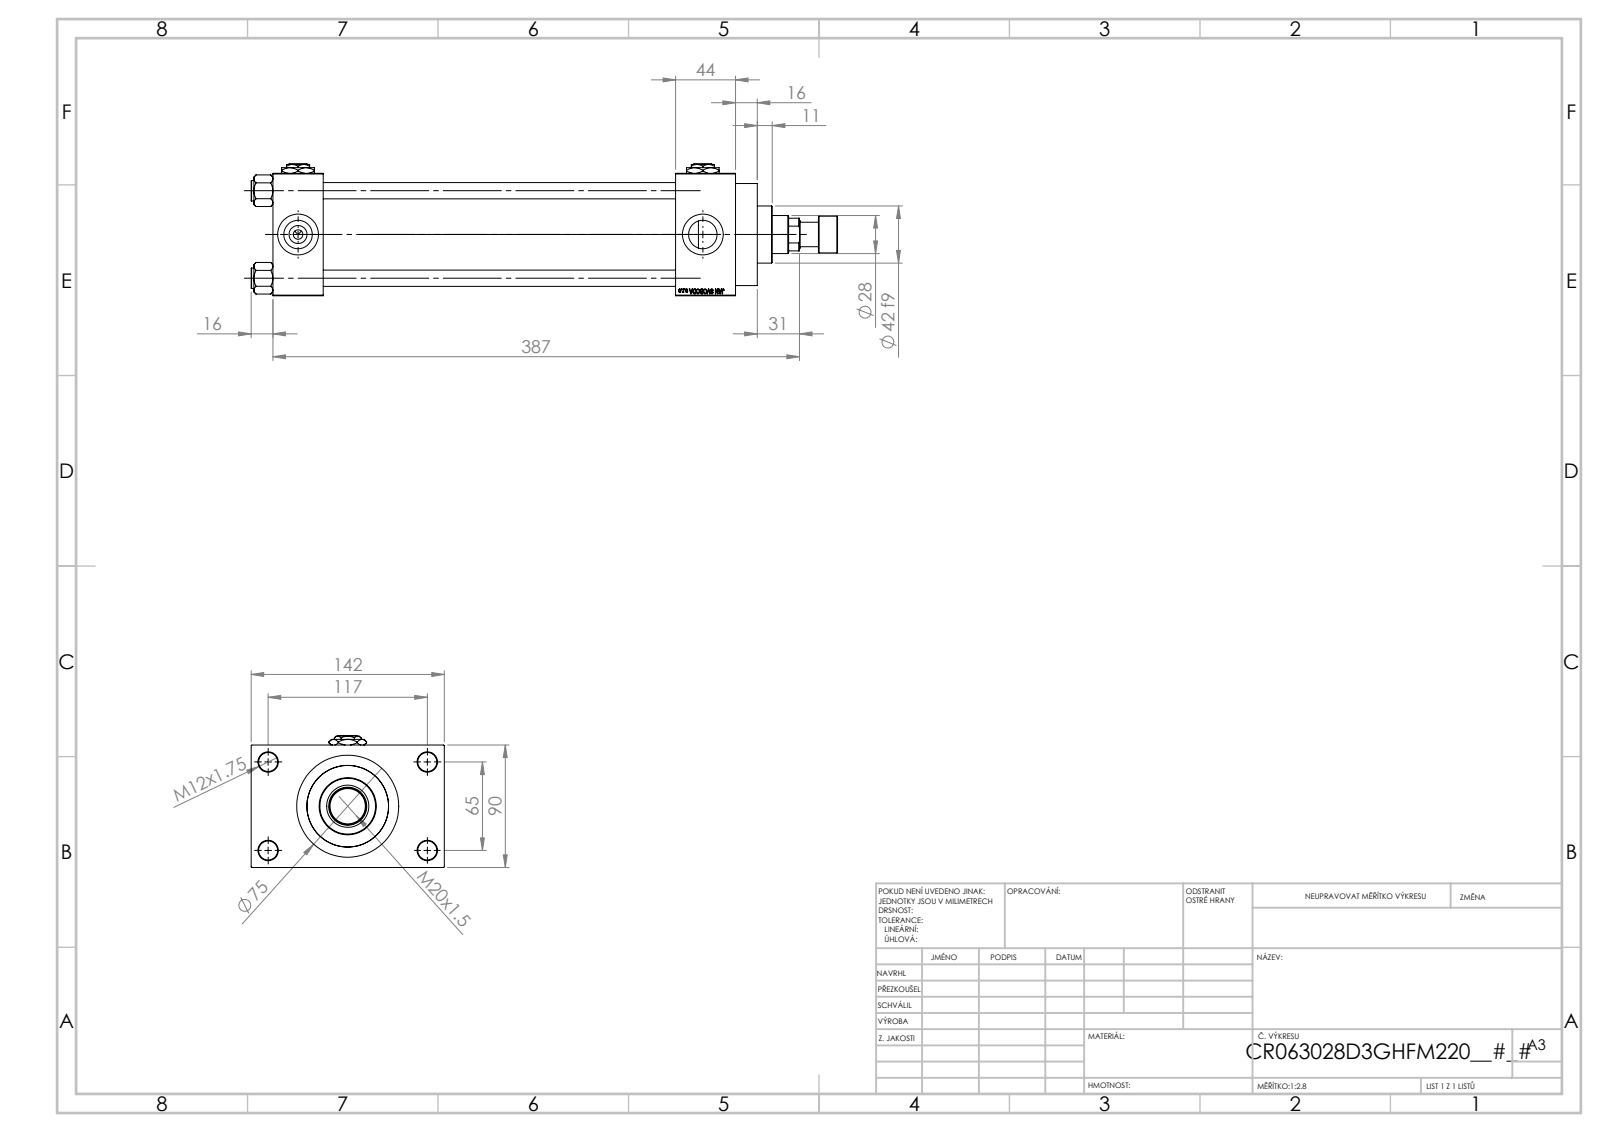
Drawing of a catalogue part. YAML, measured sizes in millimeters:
part_name: "V215CR_ROD_END_F; V215CR_D_Body; V215_VC_A; V215CR_D_TYCINKA (+3 more)"
step_written_by: "SolidWorks 2019 (CONFIG_CONTROL_DESIGN)"
units: millimeters
bodies: {solids: 14, faces: 1218, planar: 549, cylindrical: 103, other: 566}
overall_size: [431, 142, 97]
volume: 1440000
surface_area: 338888
round_holes:
  - {diameter: 12, count: 4}
  - {diameter: 14, count: 4}
  - {diameter: 20.96, count: 4}
  - {diameter: 30, count: 4}
  - {diameter: 7, count: 3}
  - {diameter: 18.5, count: 1}
  - {diameter: 28, count: 1}
  - {diameter: 31, count: 1}
  - {diameter: 50, count: 1}
  - {diameter: 60, count: 1}
  - {diameter: 63, count: 1}
round_bosses_or_shafts:
  - {diameter: 15, count: 4}
  - {diameter: 75, count: 1}
  - {diameter: 69, count: 1}
  - {diameter: 42, count: 1}
  - {diameter: 27, count: 1}
  - {diameter: 18, count: 1}
face_to_face_distances: [90, 259, 37, 296, 303, 340, 44, 26, 116, 16]
hole_center_spacings: [26.35, 45.47, 64.3, 66.92, 69.81, 90.65, 111.34, 65]
